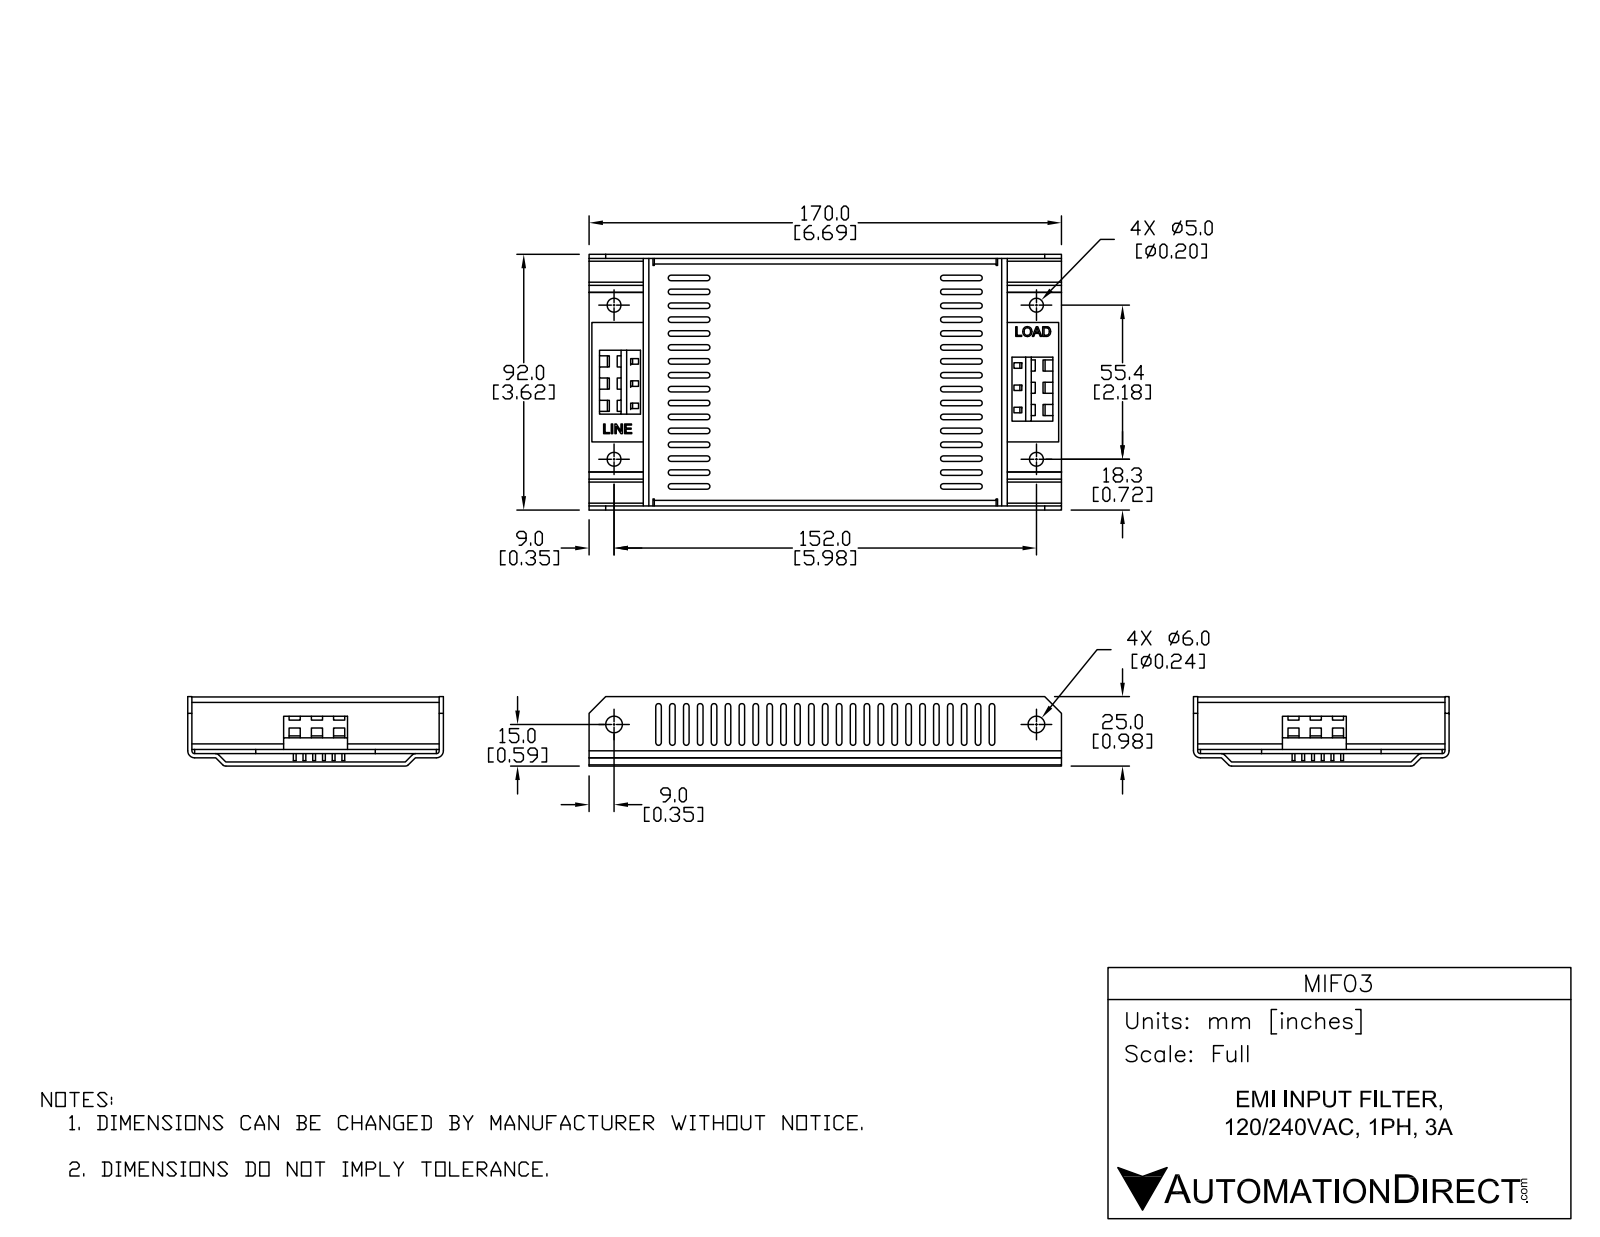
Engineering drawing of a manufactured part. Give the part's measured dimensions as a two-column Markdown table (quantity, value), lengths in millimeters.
| quantity | value |
| --- | --- |
| part name | MIF03 |
| STEP written by | SolidWorks 2017 (AUTOMOTIVE_DESIGN) |
| units | millimeters |
| bodies | 5 solids, 859 faces (451 planar, 349 cylindrical, 59 other) |
| overall size | 170 × 92 × 25 |
| volume | 71 530 mm³ |
| surface area | 108 700 mm² |
| round holes (diameter × count) | 1 × 46, 3.3 × 4, 3.5 × 4, 4 × 4, 5 × 4, 6 × 2 |
| round bosses / shafts (diameter × count) | 1 × 10 |
| partial cylindrical surfaces (radius × count) | 1 × 122, 2 × 6, 0.1 × 4, 1.5 × 4, 2.5 × 2, 2.1 × 1, 2.6 × 1, 2.8 × 1 |
| main face-to-face distances | 1.5, 4.5, 3, 1, 6, 17.9, 24.9, 23.4, 20.4, 18.9 |
| hole center spacings | 17.7, 18.7, 68.8, 138, 153.1, 15.5, 20.3, 152 |
